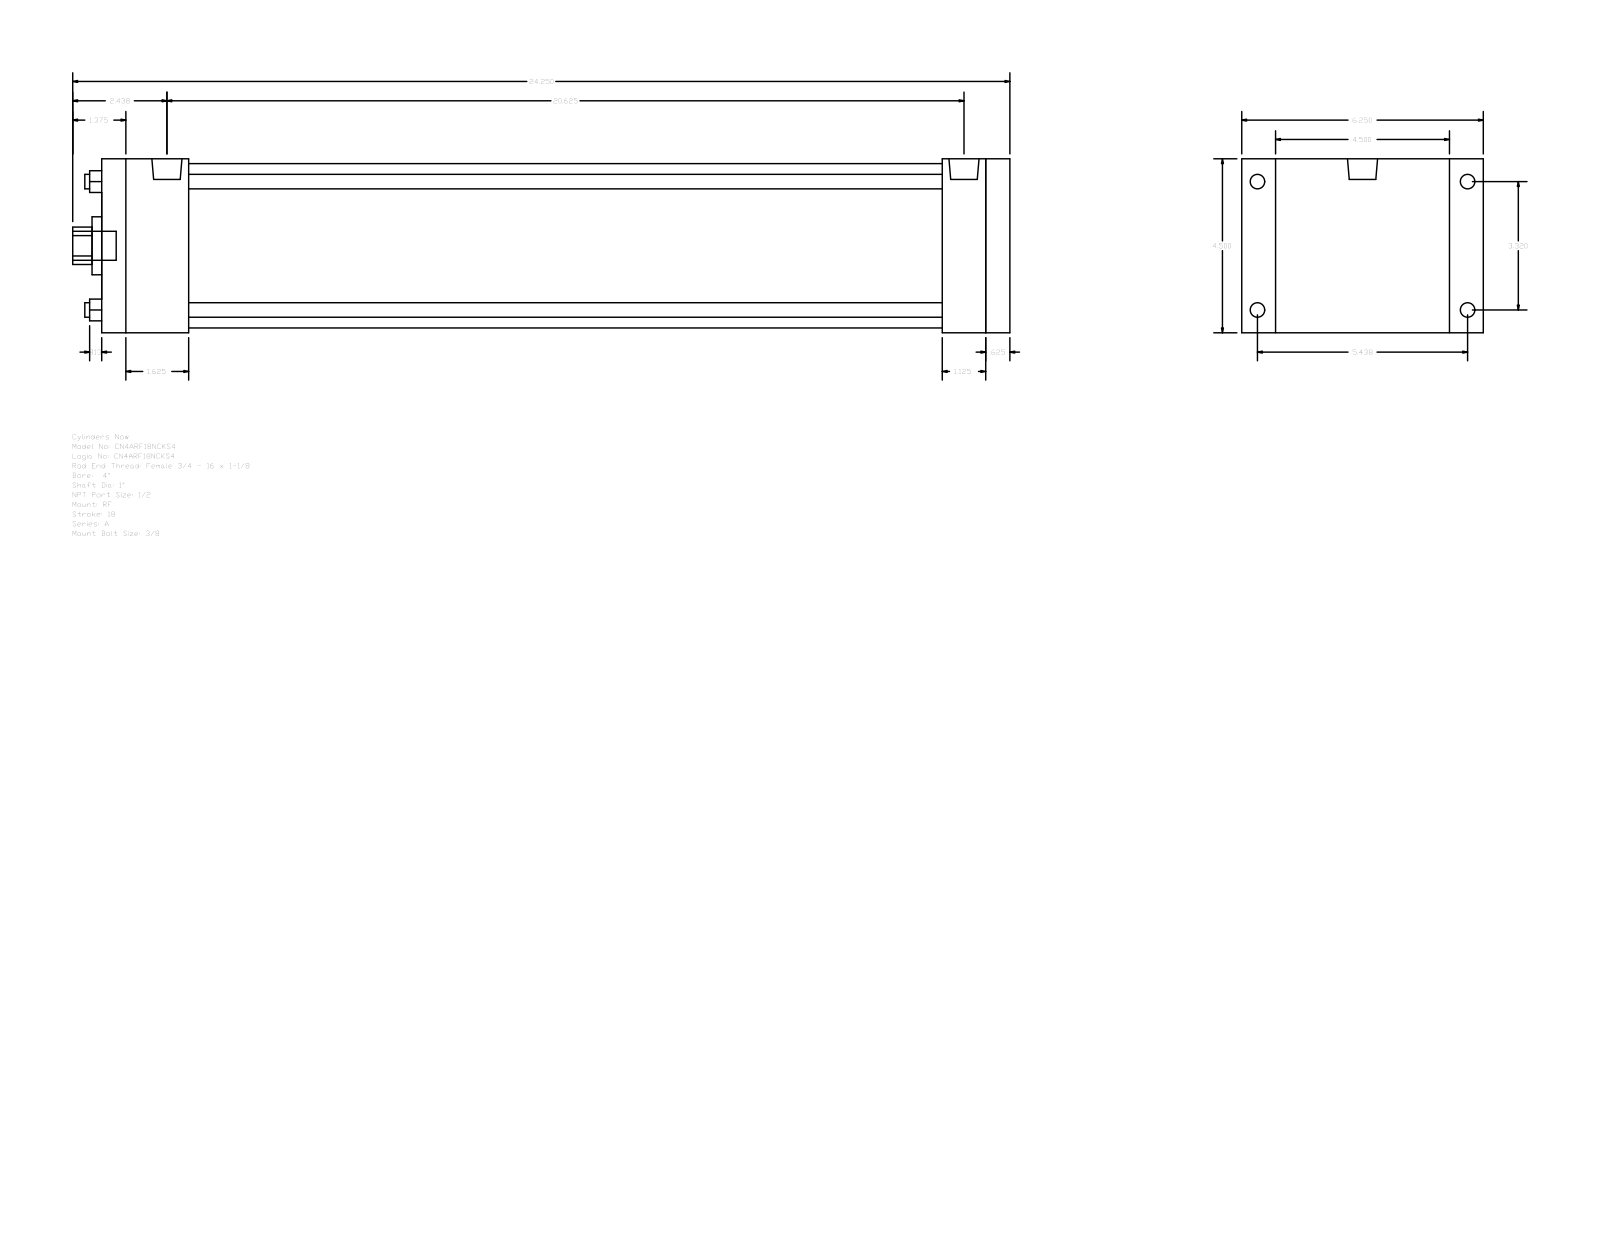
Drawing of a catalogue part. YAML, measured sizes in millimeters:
part_name: "A_RF__0400_1"
step_written_by: "GSSL Pune (CONFIG_CONTROL_DESIGN)"
units: millimeters
bodies: {solids: 0, faces: 92, planar: 64, cylindrical: 28, other: 0}
overall_size: [615.95, 158.75, 114.3]
round_holes:
  - {diameter: 9.53, count: 4}
  - {diameter: 25.4, count: 1}
  - {diameter: 38.1, count: 1}
  - {diameter: 107.95, count: 1}
round_bosses_or_shafts:
  - {diameter: 9.53, count: 4}
  - {diameter: 8.73, count: 4}
  - {diameter: 19.77, count: 2}
  - {diameter: 19.05, count: 1}
partial_cylinders:
  - {radius: 12.29, count: 1}
face_to_face_distances: [114.3, 596.9, 15.87, 581.03, 22.23, 136.53, 552.45, 28.58, 44.45, 57.15]
hole_center_spacings: [59.62, 84.32, 119.25]
